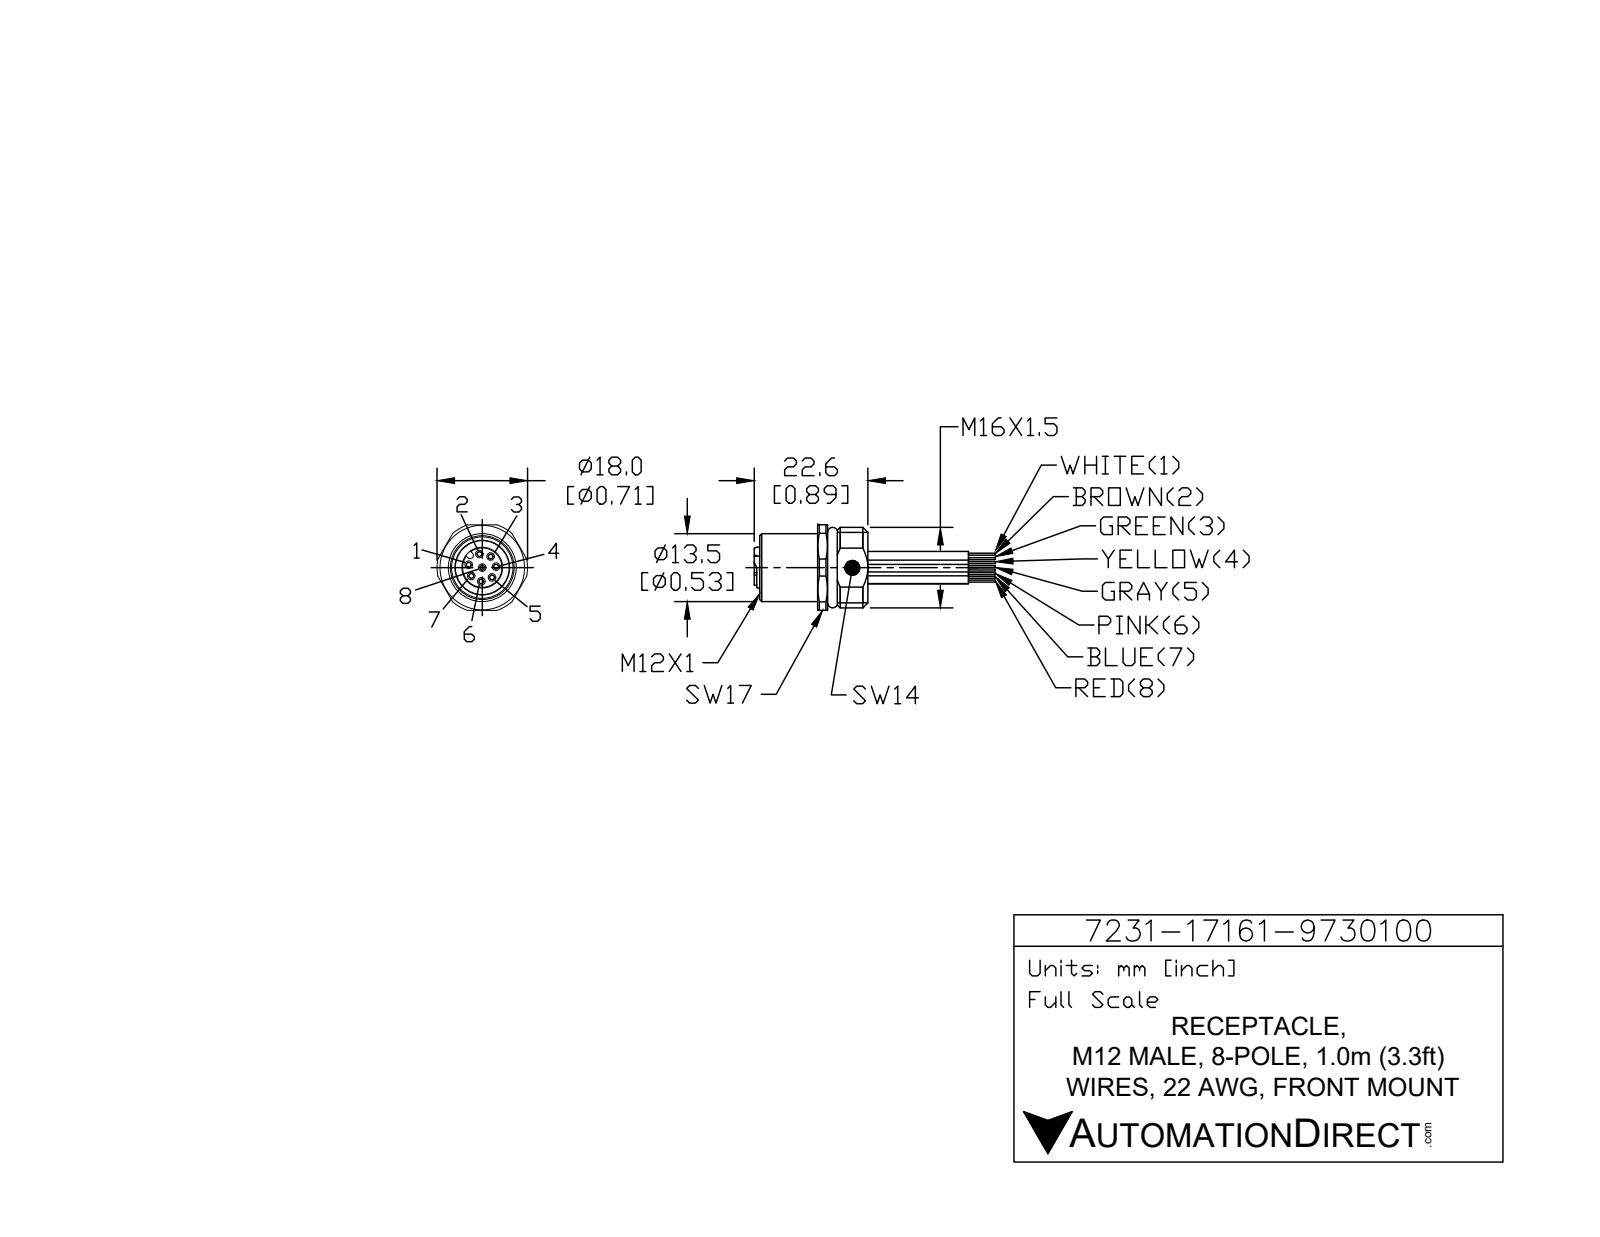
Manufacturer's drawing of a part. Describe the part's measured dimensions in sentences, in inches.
The part is named "7231-17161-9730100". Its 3-D file was written by "SolidWorks 2015 (AUTOMOTIVE_DESIGN)". It is 1 solid with 140 faces: 42 planar, 68 cylindrical and 30 other. Overall it measures 1.815 by 0.709 by 0.669 inches. Its volume is 0.209 cubic inches and its surface area 4.363 square inches. Round holes: 8 of diameter 0.067, 1 of diameter 0.327, 1 of diameter 0.512. Round bosses or shafts: 8 of diameter 0.055, 8 of diameter 0.032, 1 of diameter 0.472, 1 of diameter 0.421, 1 of diameter 0.406. Partial cylindrical surfaces (rounded edges, fillets, slot ends): 1 of radius 0.024, 1 of radius 0.315, 1 of radius 0.354. The main face-to-face distances are 0.354, 0.276, 0.079, 0.551, 0.669, 0.638, 0.362, 0.283, 0.35, 0.988. The hole center spacings are 0.108, 0.163, 0.207, 0.214, 0.089, 0.09, 0.09, 0.183.
